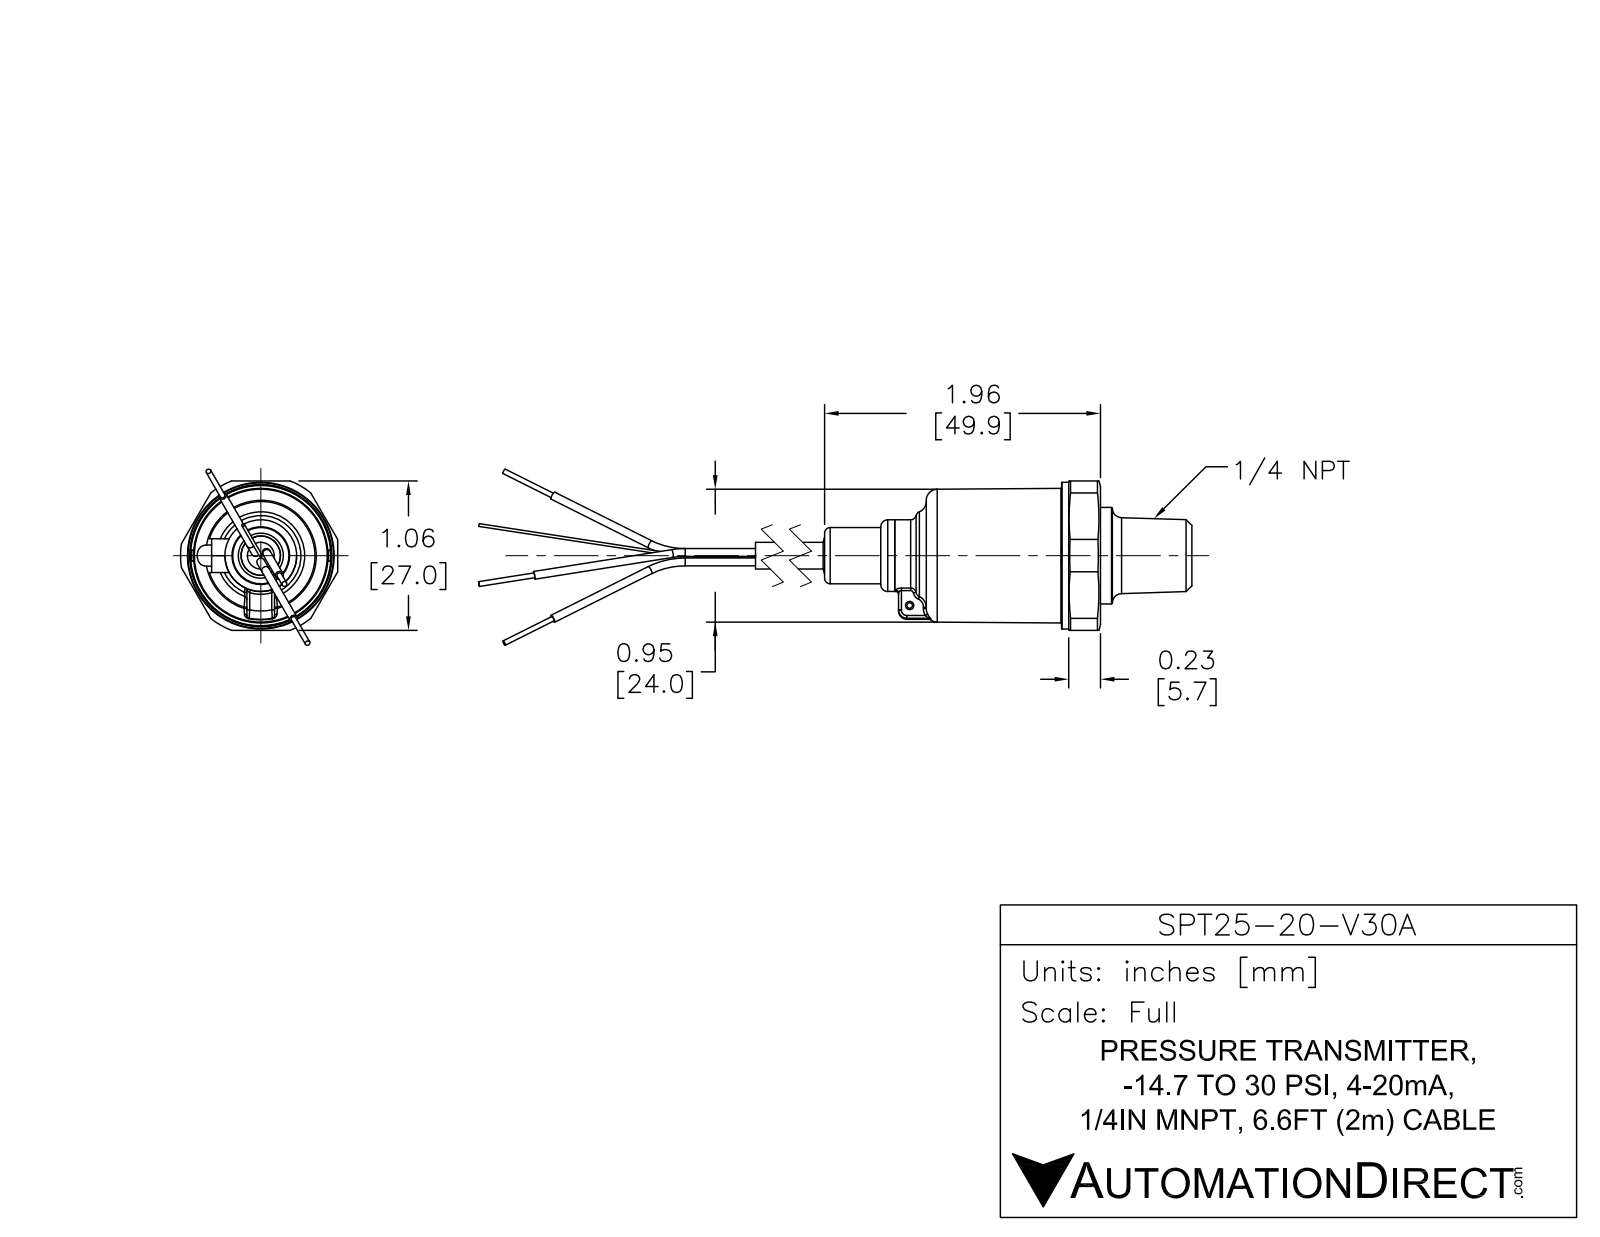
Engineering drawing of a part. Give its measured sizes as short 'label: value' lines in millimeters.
name: SPT25-20-V30A
written by: SolidWorks 2011 (AUTOMOTIVE_DESIGN)
unit: mm
bodies: 7 solids, 75 faces (32 planar, 27 cylindrical, 16 other)
size: 153.3 × 29 × 27.09
volume: 20 801 mm³; area: 7 170 mm²
holes: 1× ⌀1, 1× ⌀3.3
bosses: 6× ⌀1.4, 5× ⌀0.75, 1× ⌀26.75, 1× ⌀24, 1× ⌀17.5, 1× ⌀14, 1× ⌀13, 1× ⌀10
rounds: 1× R2, 1× R14.5
face distances: 6.75, 24, 17.25, 42.75, 49.5, 66.75, 44, 1.25, 5.5, 22.75
